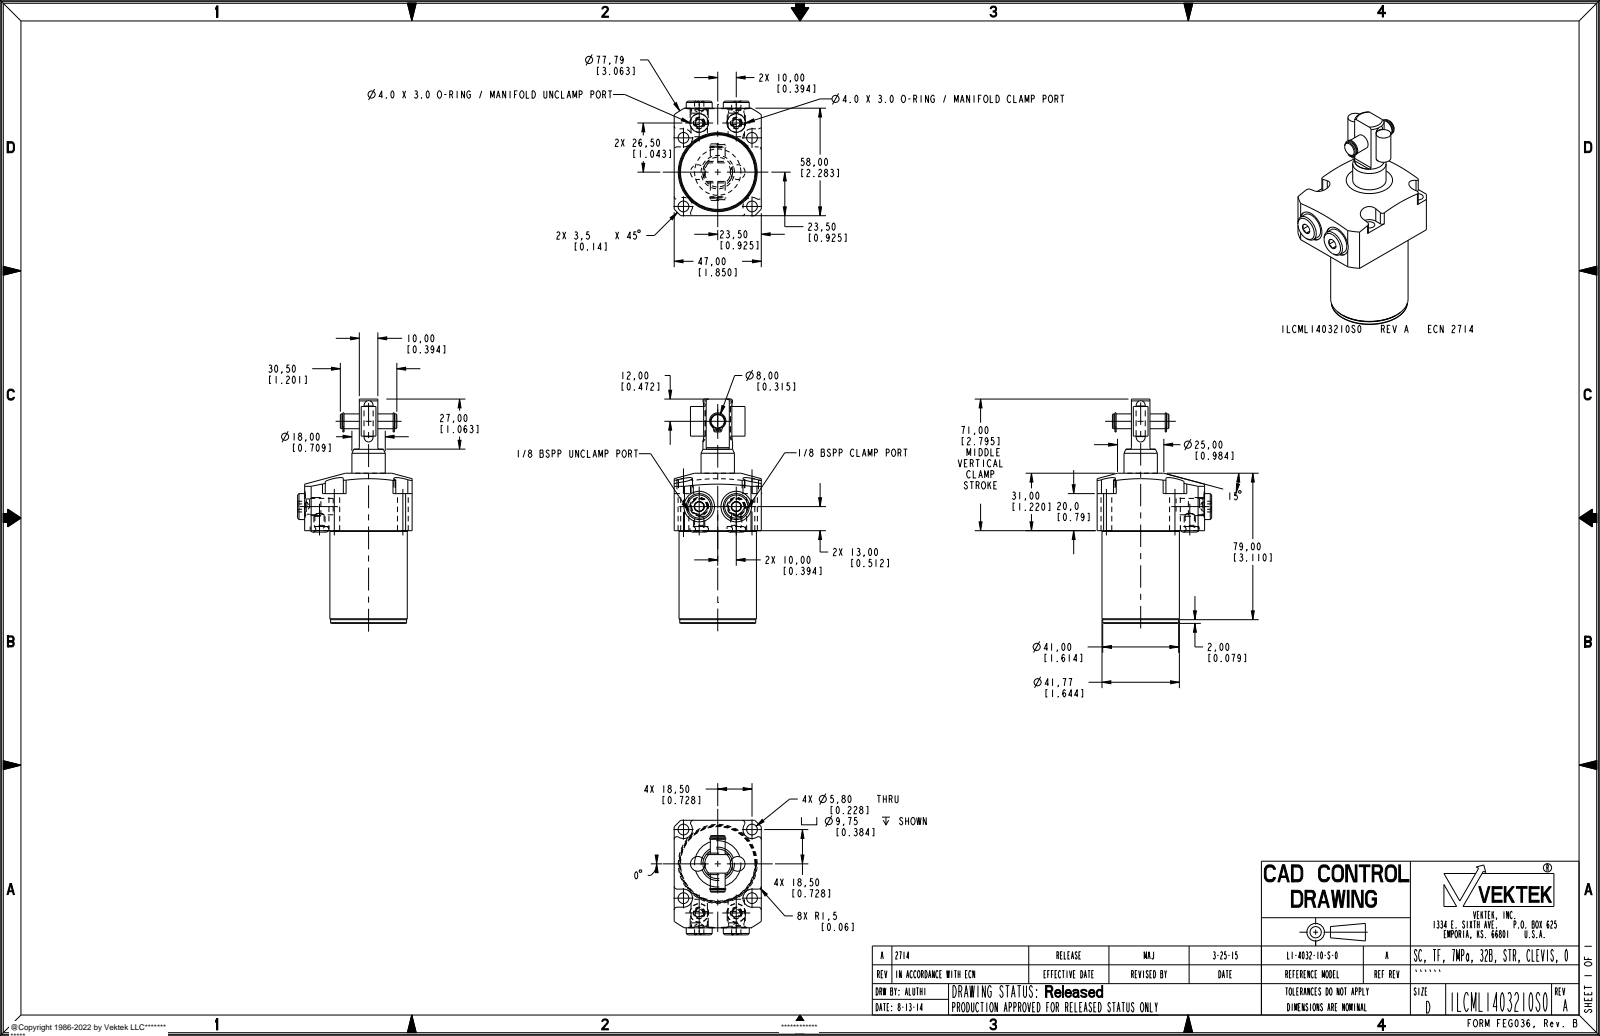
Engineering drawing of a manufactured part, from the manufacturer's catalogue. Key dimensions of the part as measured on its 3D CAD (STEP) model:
Part name (STEP PRODUCT): ILCML1403210S0
STEP written by: PRO/ENGINEER BY PARAMETRIC TECHNOLOGY CORPORATION, 2013320 (AUTOMOTIVE_DESIGN)
Units: millimetres
Bodies: 5 solids, 245 faces (85 planar, 104 cylindrical, 56 other)
Overall size (bounding box): 121 × 61.81 × 47
Volume: 149 822 mm³ · Surface area: 25 587 mm²
Round holes (diameter × count): ⌀5 ×4, ⌀5.8 ×4, ⌀1.04 ×2, ⌀8.84 ×2, ⌀10 ×2, ⌀16.5 ×2
Round bosses / shafts (diameter × count): ⌀14 ×2, ⌀9.73 ×2, ⌀8.25 ×2, ⌀7.95 ×2, ⌀6 ×2, ⌀41.77 ×1, ⌀41 ×1, ⌀18 ×1
Partial cylindrical surfaces — rounded edges, fillets, slot ends (radius × count): R1.5 ×8, R4.88 ×4, R0.8 ×2, R1.04 ×2, R2.32 ×2, R3.98 ×2, R4.37 ×1, R38.9 ×1
Main face-to-face distances: 47, 50, 58, 20, 31, 10, 28.5, 18.5, 39.5, 29.5
Hole centre spacings: 37, 11.67, 20, 29.6, 42.2, 42.75, 45.8, 52.33
